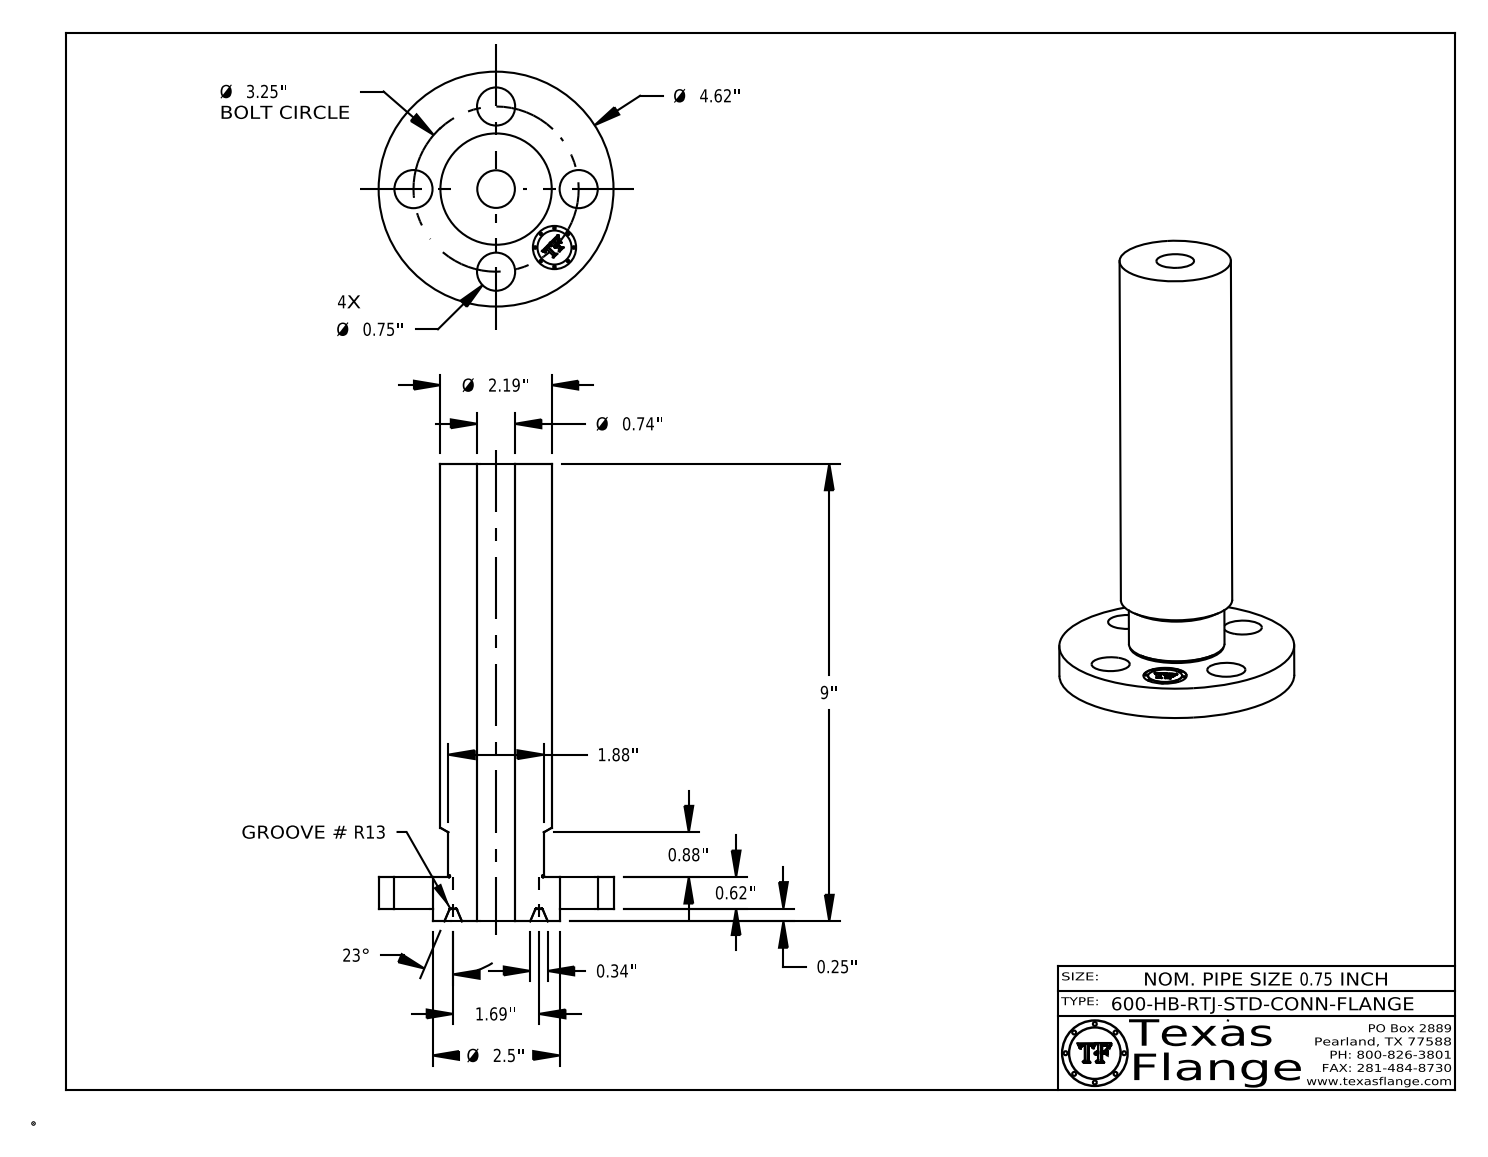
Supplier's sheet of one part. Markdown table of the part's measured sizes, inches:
| quantity | value |
| --- | --- |
| part name | 0.75-600-HB-RTJ-STD-CONN-FLANGE |
| STEP written by | CATIA V5 STEP AP214 (AUTOMOTIVE_DESIGN) |
| units | inches |
| bodies | 1 solid, 423 faces (371 planar, 38 cylindrical, 14 other) |
| overall size | 9 × 4.62 × 4.62 |
| volume | 36.04 in³ |
| surface area | 125.4 in² |
| round holes (diameter × count) | 0.75 × 4, 0.74 × 1, 0.85 × 1 |
| round bosses / shafts (diameter × count) | 0.051 × 8, 4.62 × 1, 2.5 × 1, 2.19 × 1, 1.88 × 1, 0.67 × 1 |
| main face-to-face distances | 0.62, 8.75, 8.13, 0.25, 0.87, 9, 0.865, 0.615, 8.135, 0.254 |
| hole center spacings | 1.625, 2.298, 1.244, 3.003, 3.25 |
